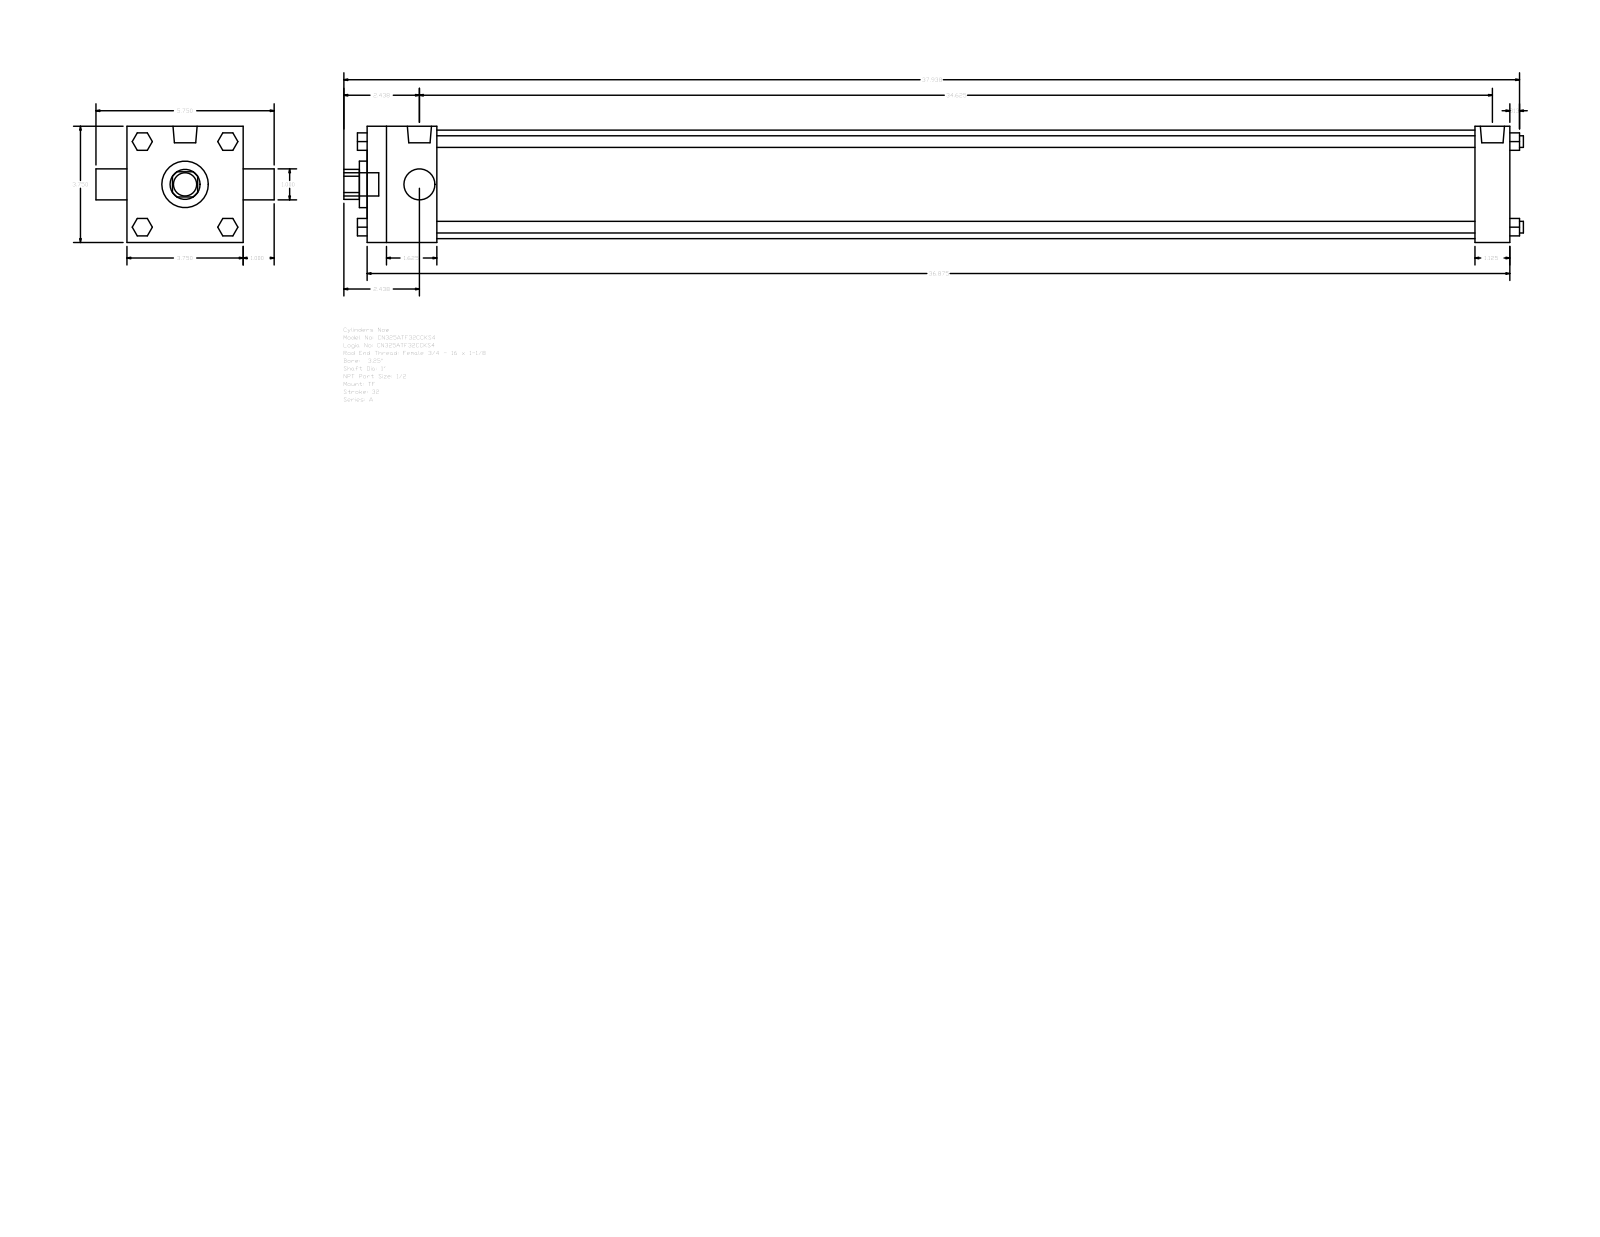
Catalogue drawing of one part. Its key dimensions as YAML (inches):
part_name: "A_TF__0325_1"
step_written_by: "GSSL Pune (CONFIG_CONTROL_DESIGN)"
units: inches
bodies: {solids: 0, faces: 120, planar: 92, cylindrical: 28, other: 0}
overall_size: [38.063, 5.75, 3.75]
round_holes:
  - {diameter: 1, count: 2}
  - {diameter: 1.5, count: 1}
  - {diameter: 3.5, count: 1}
round_bosses_or_shafts:
  - {diameter: 0.375, count: 4}
  - {diameter: 0.344, count: 3}
  - {diameter: 0.778, count: 2}
  - {diameter: 0.75, count: 1}
partial_cylinders:
  - {radius: 0.484, count: 1}
face_to_face_distances: [3.75, 36.875, 1.125, 2.25, 35.75, 33.5, 34.625, 0.562, 1.38, 2.39]
